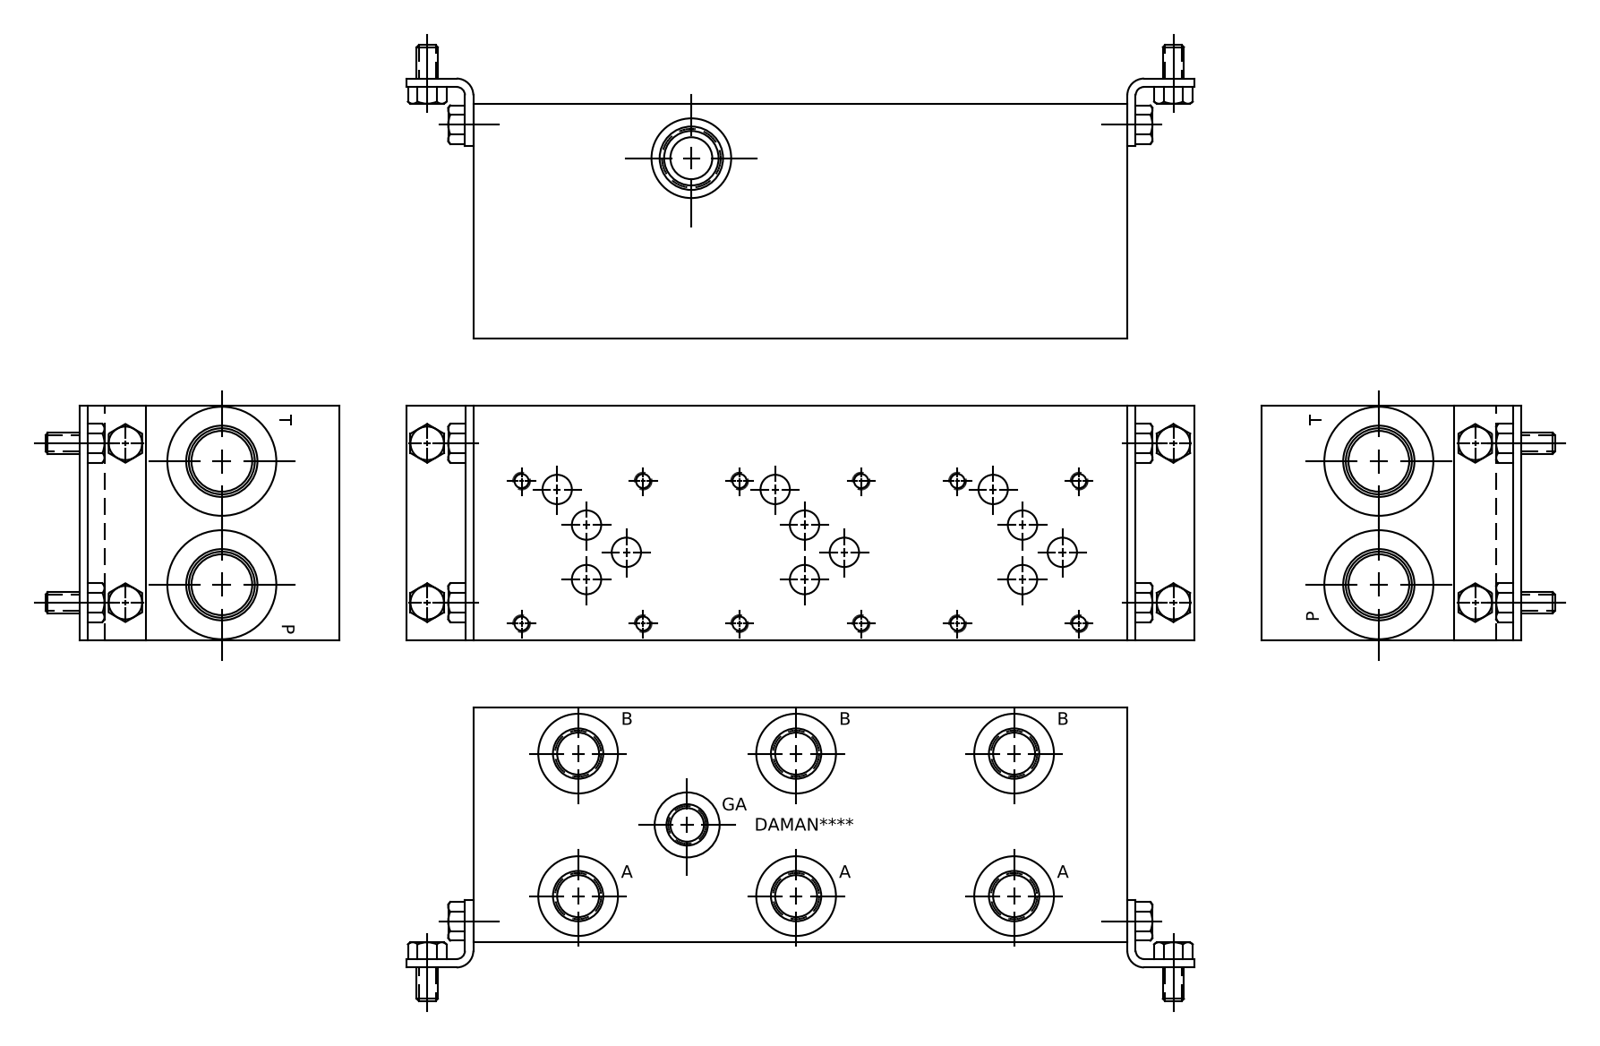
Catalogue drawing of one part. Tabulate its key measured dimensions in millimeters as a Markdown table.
| quantity | value |
| --- | --- |
| part name | Part_AD05P033S~C_3D |
| STEP written by | Autodesk Inventor 2019 (AUTOMOTIVE_DESIGN) |
| units | millimeters |
| bodies | 1 solid, 785 faces (400 planar, 105 cylindrical, 280 other) |
| overall size | 247.65 × 88.9 × 88.9 |
| volume | 1 812 000 mm³ |
| surface area | 134 370 mm² |
| round holes (diameter × count) | 5.11 × 12, 6.35 × 12, 11.13 × 12, 15.88 × 6, 17.5 × 6, 19.05 × 6, 19.25 × 6, 30.63 × 6, 6.53 × 2, 7.92 × 2, 23.01 × 2, 24.92 × 2 |
| main face-to-face distances | 88.9, 0.79, 247.65, 88.11, 246.86, 246.07, 19.05, 19.84, 227.81, 227.02 |
| hole center spacings | 82.55, 98.63, 165.1, 46.05, 70.95, 53.98, 18.27, 29.74 |
